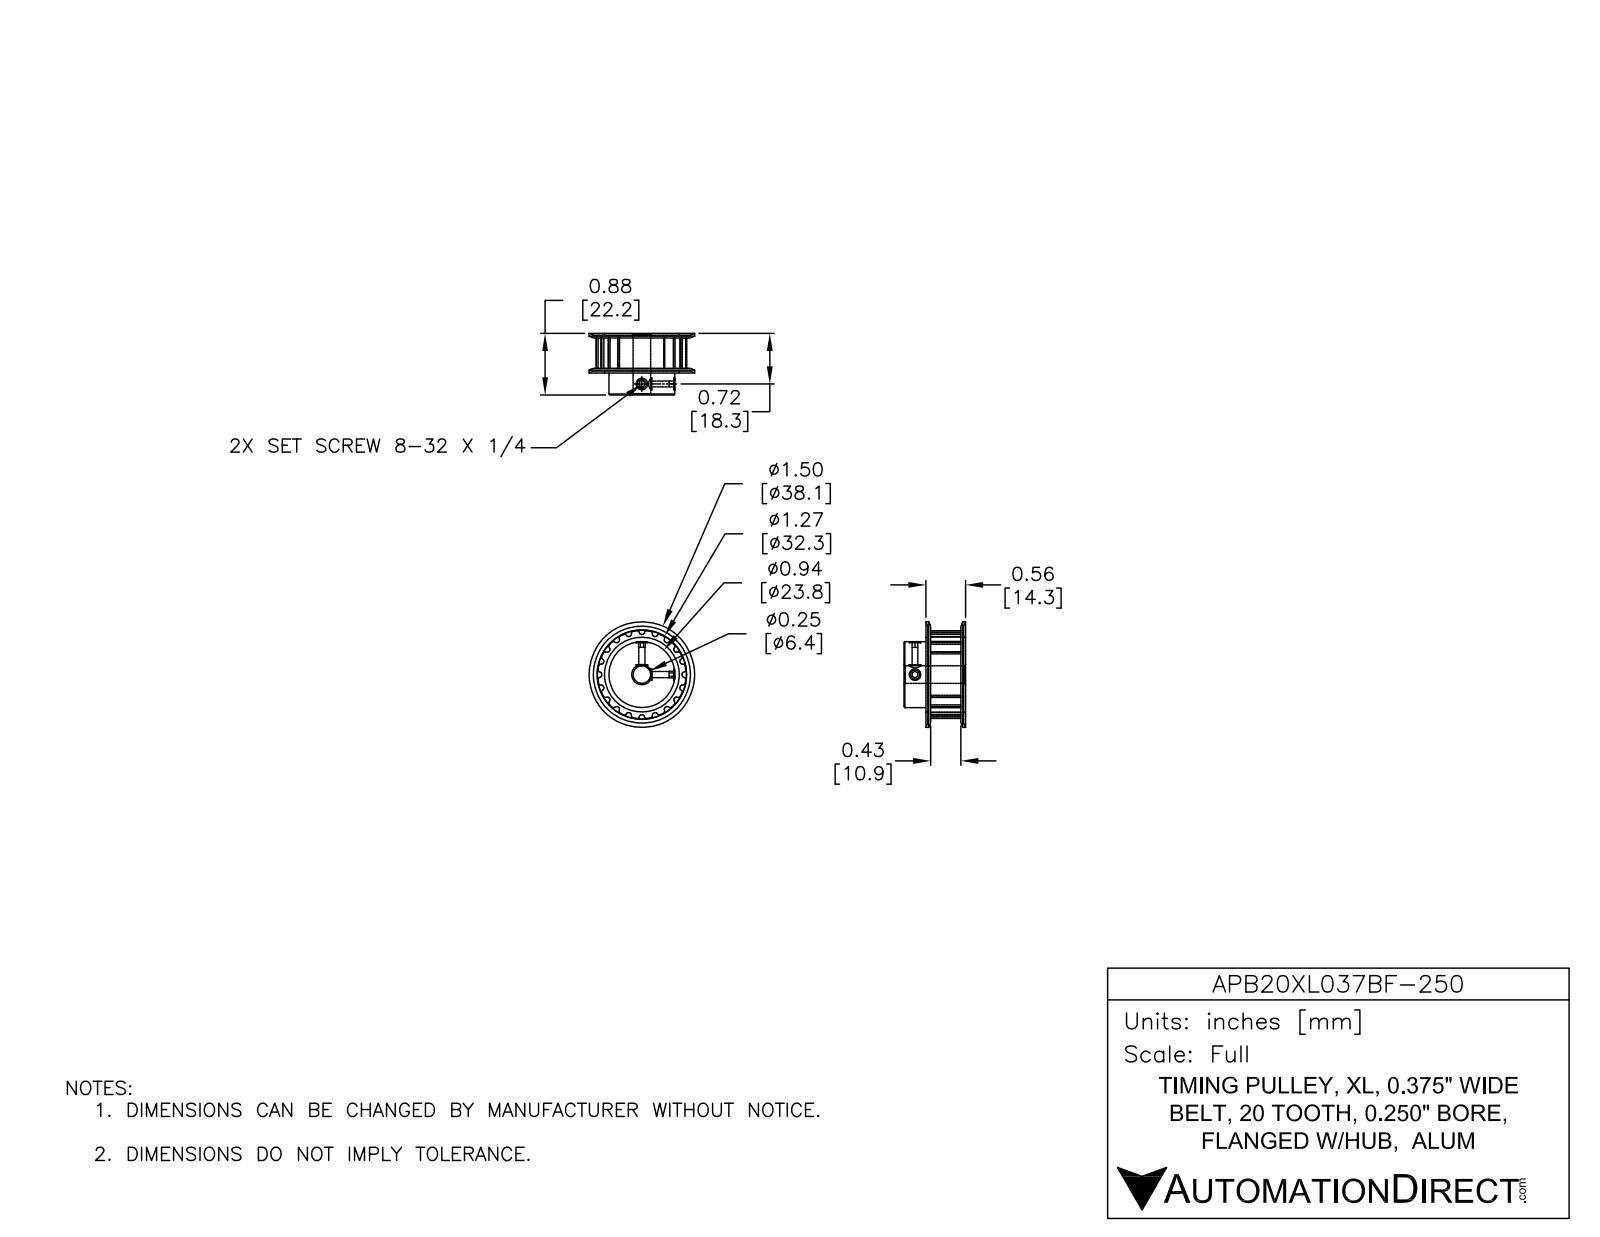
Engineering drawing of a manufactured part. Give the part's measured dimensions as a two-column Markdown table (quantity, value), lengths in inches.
| quantity | value |
| --- | --- |
| part name | APB20XL037BF-250 |
| STEP written by | SolidWorks 2014 (AUTOMOTIVE_DESIGN) |
| units | inches |
| bodies | 1 solid, 214 faces (66 planar, 126 cylindrical, 22 other) |
| overall size | 1.5 × 1.5 × 0.875 |
| volume | 0.824 in³ |
| surface area | 9.095 in² |
| round holes (diameter × count) | 0.088 × 2, 0.25 × 1 |
| round bosses / shafts (diameter × count) | 0.938 × 1 |
| partial cylindrical surfaces (radius × count) | 0.015 × 80, 0.572 × 1 |
| main face-to-face distances | 0.033, 0.495, 0.875, 0.528, 0.348, 0.843, 1.253, 0.437, 0.065, 0.032 |
